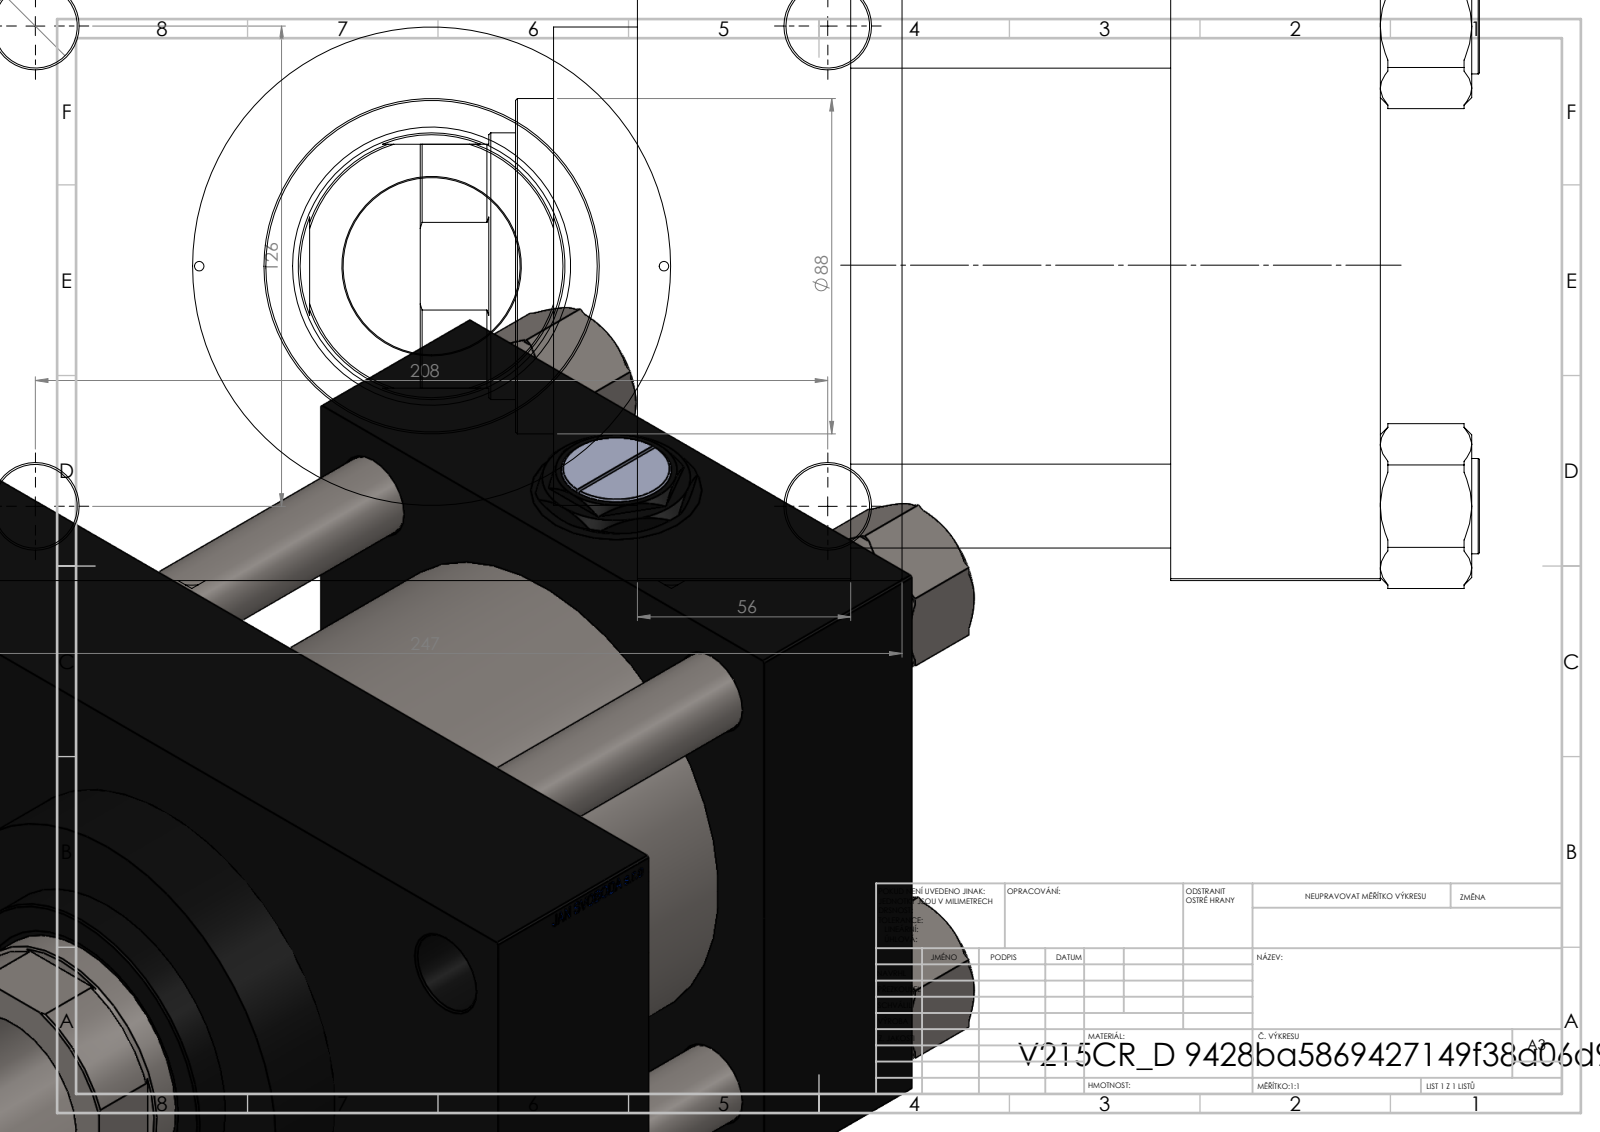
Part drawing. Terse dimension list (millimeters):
name: Zatka_pro_OIL_PORT; V215CR_D_Body; V215CR_D_TYCINKA; V215_VC_A (+2 more)
written by: SolidWorks 2019 (CONFIG_CONTROL_DESIGN)
unit: mm
bodies: 12 solids, 1207 faces (570 planar, 97 cylindrical, 540 other)
size: 278 × 247 × 174.07
volume: 5 009 000 mm³; area: 548 090 mm²
holes: 8× ⌀22, 3× ⌀7, 3× ⌀32.24, 3× ⌀45, 2× ⌀2.5, 1× ⌀46.5, 1× ⌀70, 1× ⌀73, 1× ⌀96, 1× ⌀125, 1× ⌀125.5
bosses: 4× ⌀25, 1× ⌀131, 1× ⌀88
rounds: 1× R34
face distances: 165, 84, 55, 139, 56, 195, 140, 41, 206, 173.74
hole spacings: 41.05, 62.98, 76.28, 89.02, 121.59, 125.9, 132.47, 139.02
